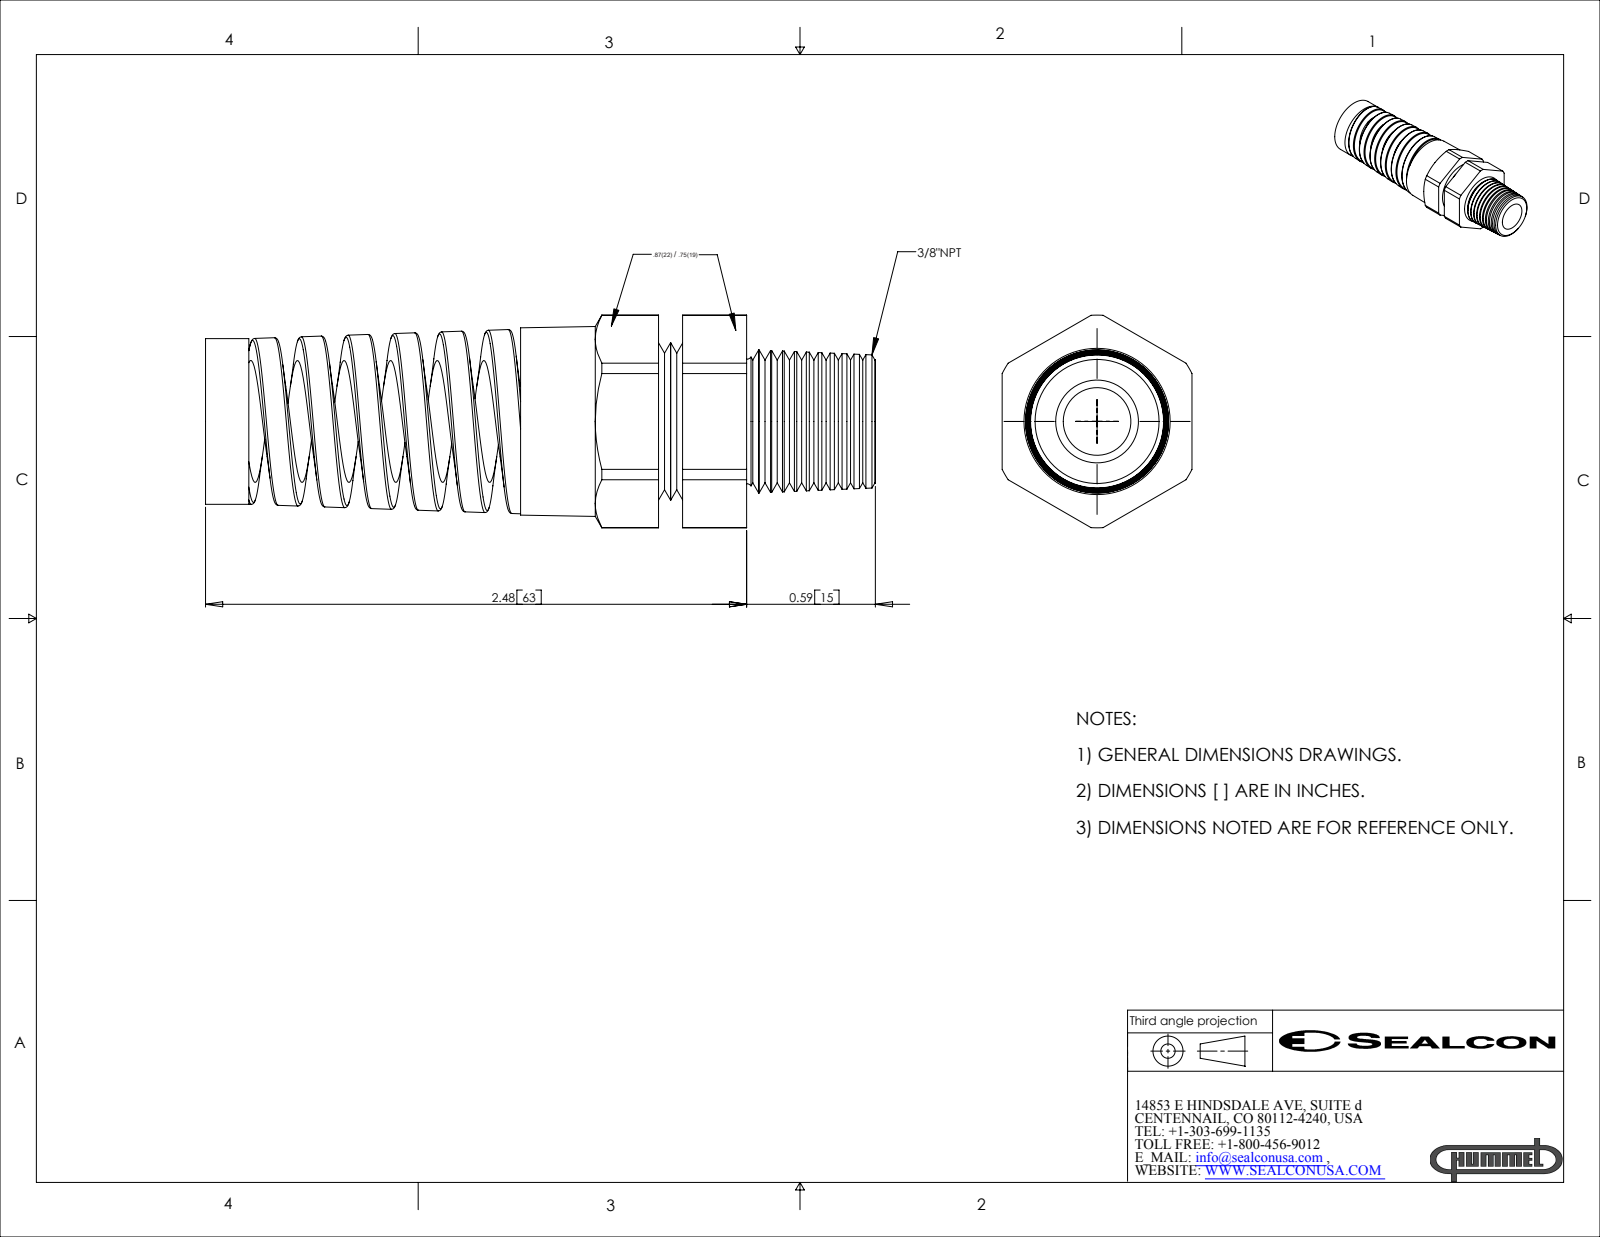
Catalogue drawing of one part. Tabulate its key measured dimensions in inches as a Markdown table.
| quantity | value |
| --- | --- |
| part name | CF09NA-GY |
| STEP written by | SolidWorks 2007 (CONFIG_CONTROL_DESIGN) |
| units | inches |
| bodies | 1 solid, 158 faces (19 planar, 34 cylindrical, 105 other) |
| overall size | 3.07 × 0.974 × 0.87 |
| volume | 0.868 in³ |
| surface area | 15.19 in² |
| round holes (diameter × count) | 0.31 × 1, 0.559 × 1, 0.721 × 1 |
| round bosses / shafts (diameter × count) | 0.759 × 1 |
| partial cylindrical surfaces (radius × count) | 0.487 × 1 |
| main face-to-face distances | 0.87, 1.036, 0.632, 0.404, 0.742, 0.11, 0.294, 1.444, 2.076, 2.186 |
